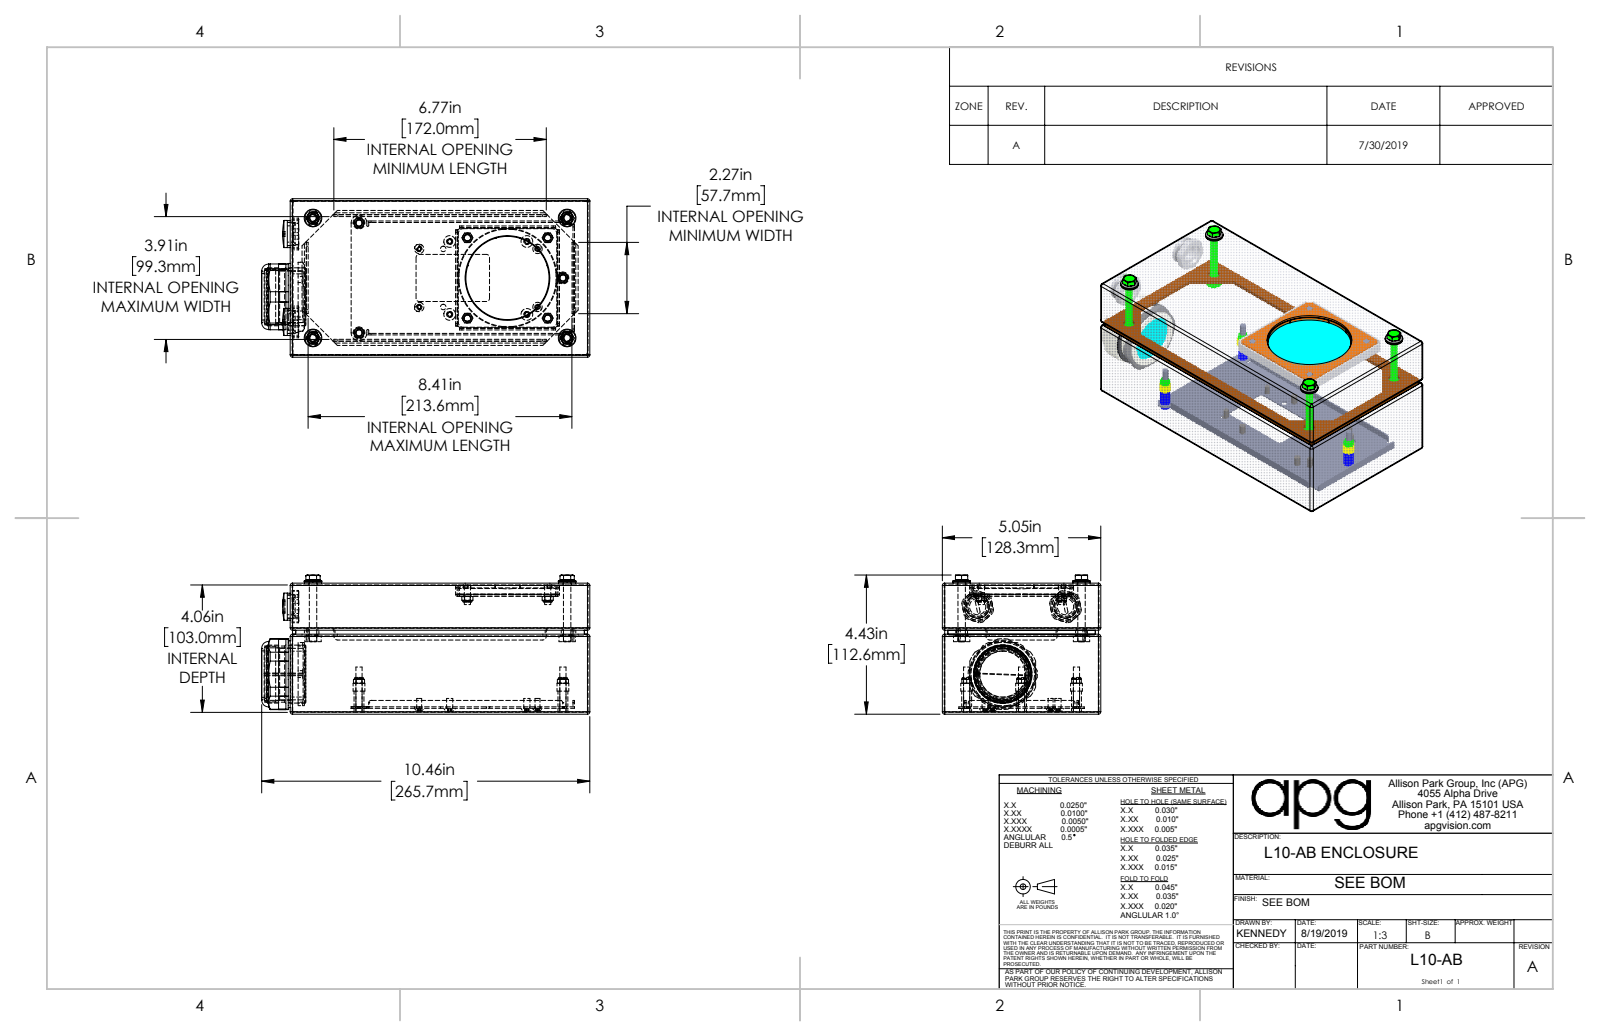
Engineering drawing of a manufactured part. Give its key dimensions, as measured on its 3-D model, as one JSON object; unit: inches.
{"part_name": "PG11-TPp; M5x.625 Stud; L10-LBody002 (L10 LOWER BODY); SM6 CLINCH NUT (+8 more)", "step_written_by": "SolidWorks 2018 (CONFIG_CONTROL_DESIGN)", "units": "inches", "bodies": {"solids": 62, "faces": 1176, "planar": 523, "cylindrical": 445, "other": 208}, "overall_size": [10.46, 5.05, 4.432], "volume_in3": 25.57, "surface_area_in2": 684.9, "round_holes": [[0.2, 7], [0.175, 6], [0.219, 4], [0.226, 4], [0.232, 4], [0.236, 4], [0.313, 4], [0.375, 4], [0.196, 3], [0.225, 2], [0.275, 2], [0.275, 2]], "round_bosses_or_shafts": [[0.197, 11], [0.29, 7], [0.562, 4], [0.546, 4], [0.52, 4], [0.394, 4], [0.295, 4], [0.157, 4]], "partial_cylinders_radius": [[0.075, 32], [0.1, 8], [0.087, 6], [0.018, 4], [0.042, 4], [0.06, 4], [0.066, 4], [0.125, 4]], "face_to_face_distances": [0.06, 4.115, 0.06, 4.055, 4.175, 0.185, 4.93, 2.55, 4.99, 5.05], "hole_center_spacings": [1.633, 1.81, 2.56, 0.577, 0.674, 0.848, 1.315, 1.369]}
